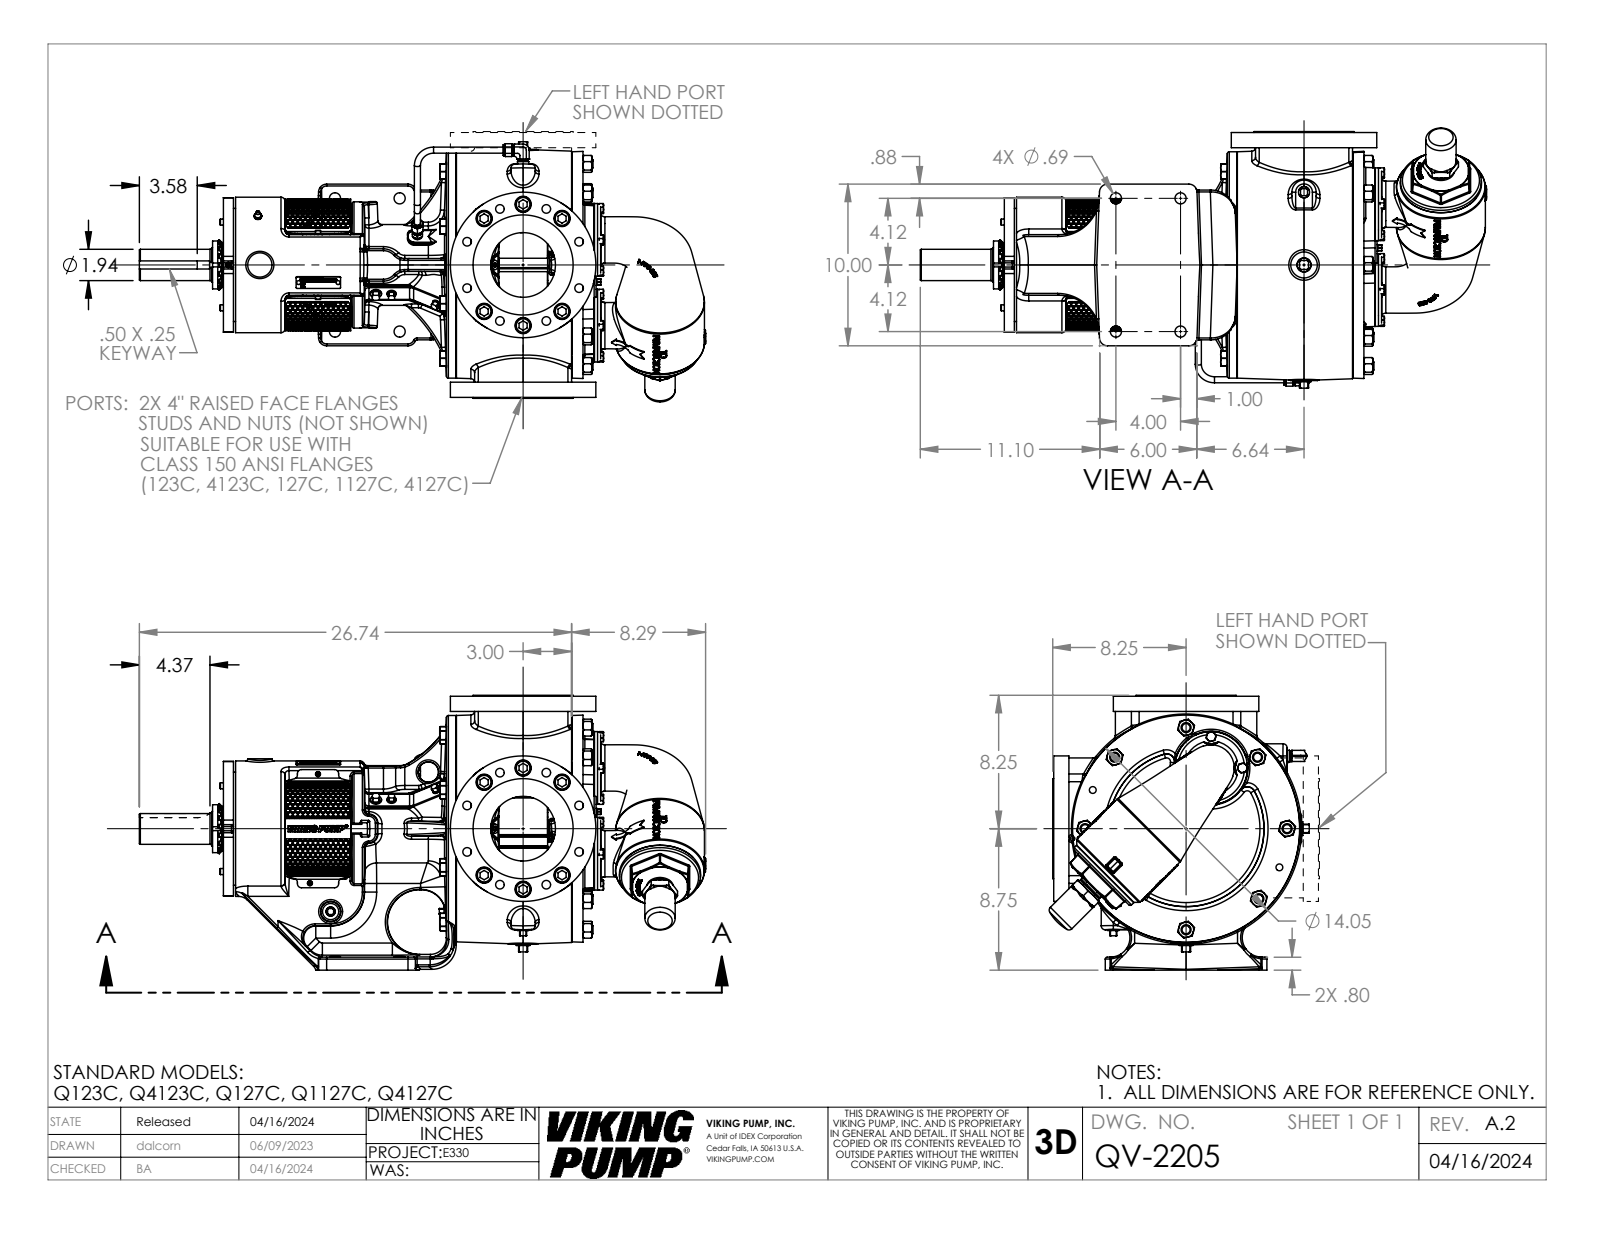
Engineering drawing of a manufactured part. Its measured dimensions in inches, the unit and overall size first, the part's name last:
Units: inches
Overall size (bounding box): 35.043 × 17 × 16.216
Round holes (diameter × count): ⌀0.531 ×16, ⌀1 ×12, ⌀0.266 ×8, ⌀1.157 ×8, ⌀0.25 ×6, ⌀0.688 ×4, ⌀0.159 ×2, ⌀0.313 ×2, ⌀0.33 ×2, ⌀4 ×2, ⌀0.213 ×1, ⌀0.453 ×1
Round bosses / shafts (diameter × count): ⌀0.937 ×12, ⌀0.617 ×8, ⌀0.437 ×3, ⌀0.312 ×3, ⌀9 ×2, ⌀6.19 ×2, ⌀4.5 ×2, ⌀0.375 ×2
Partial cylindrical surfaces — rounded edges, fillets, slot ends (radius × count): R0.12 ×60, R0.06 ×30, R0.25 ×29, R0.5 ×23, R0.015 ×18, R0.092 ×18, R0.75 ×16, R0.03 ×12
Main face-to-face distances: 0.94, 3.75, 0.5, 0.06, 1, 21.756, 22.256, 16.94, 18.006, 18.506
Hole centre spacings: 3.75, 5.303, 2.87, 6.929, 2.079, 5.783, 7.5, 1.463
Volume: 2 296 in³ · Surface area: 2 226 in²
Bodies: 1 solid, 8567 faces (3191 planar, 737 cylindrical, 4639 other)
Part name (STEP PRODUCT): QV-2205
STEP written by: SolidWorks 2022 (AUTOMOTIVE_DESIGN)
